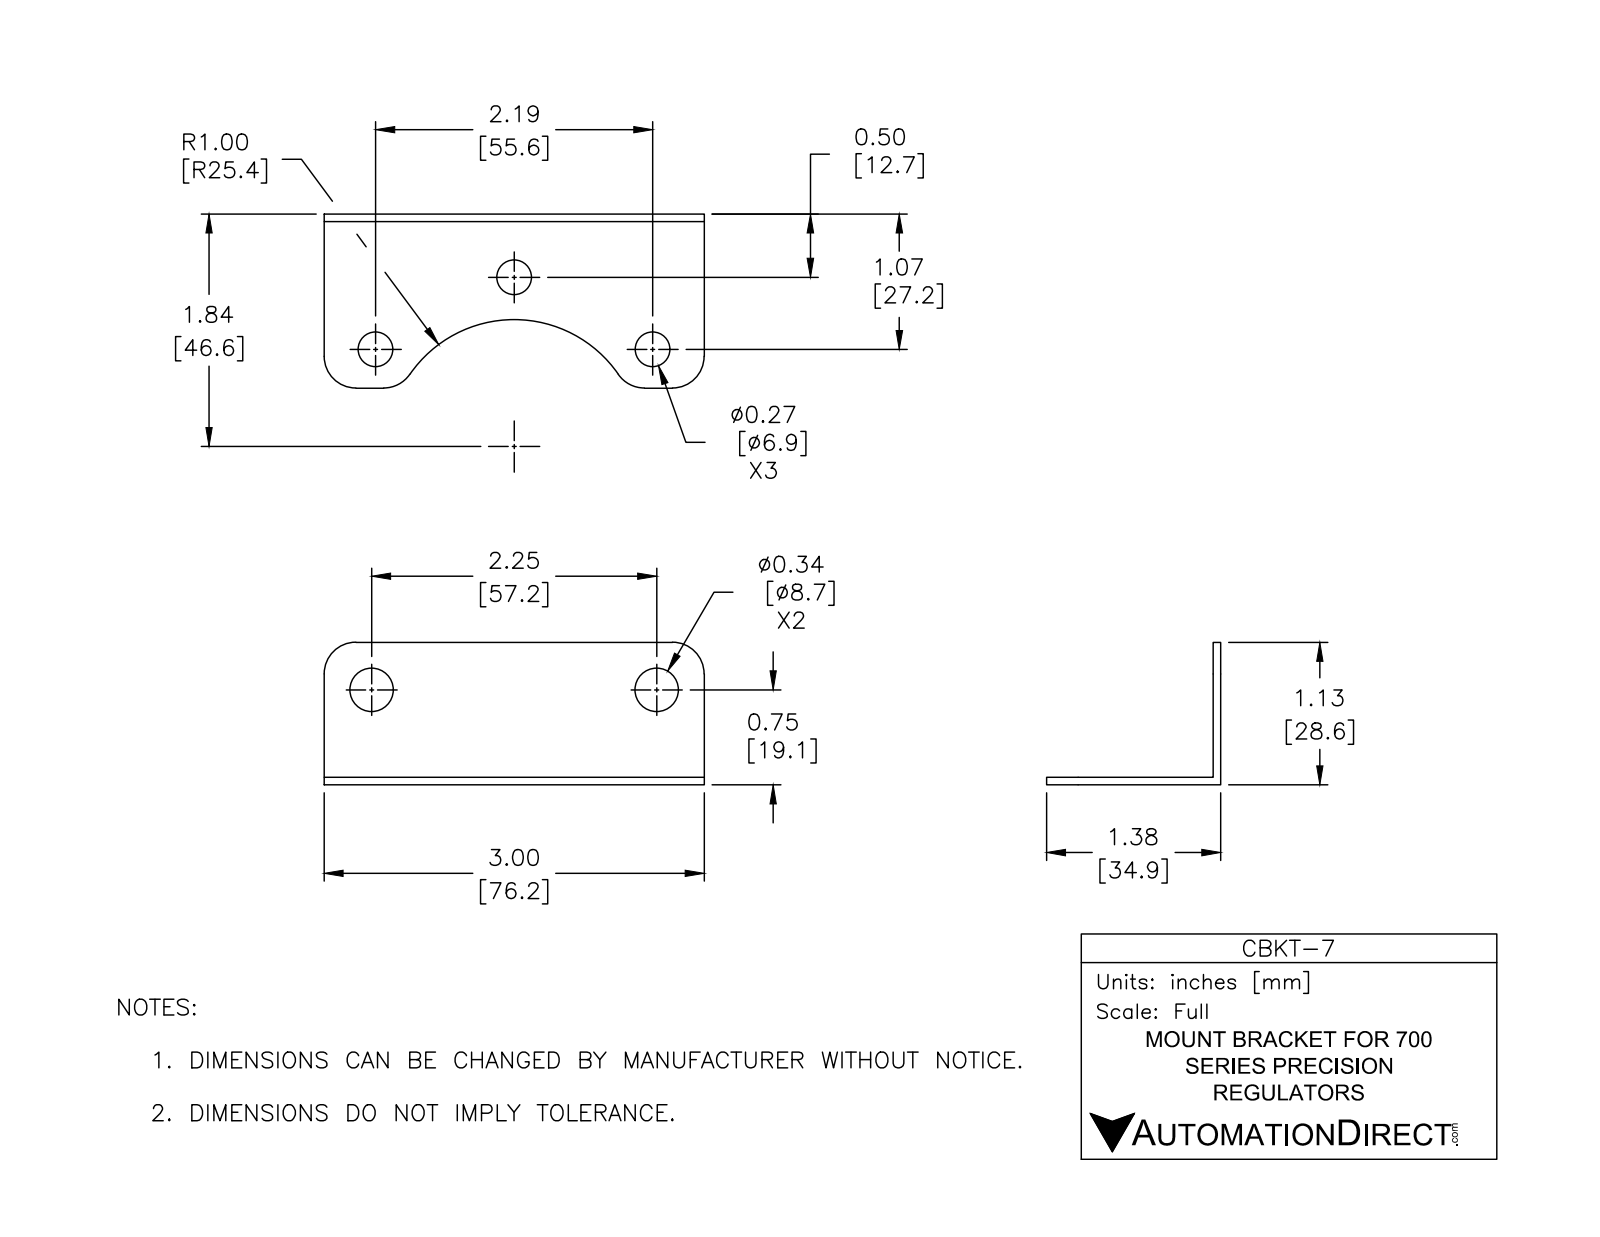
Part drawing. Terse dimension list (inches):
name: 707025
written by: Autodesk Inventor 2014 (AUTOMOTIVE_DESIGN)
unit: in
bodies: 1 solid, 21 faces (9 planar, 12 cylindrical, 0 other)
size: 3 × 1.375 × 1.125
volume: 0.373 in³; area: 13.37 in²
holes: 3× ⌀0.272, 2× ⌀0.343
rounds: 6× R0.25, 1× R1
face distances: 0.06, 1.125, 1.065, 3, 1.375, 1.315
hole spacings: 1.233, 2.187, 2.25
